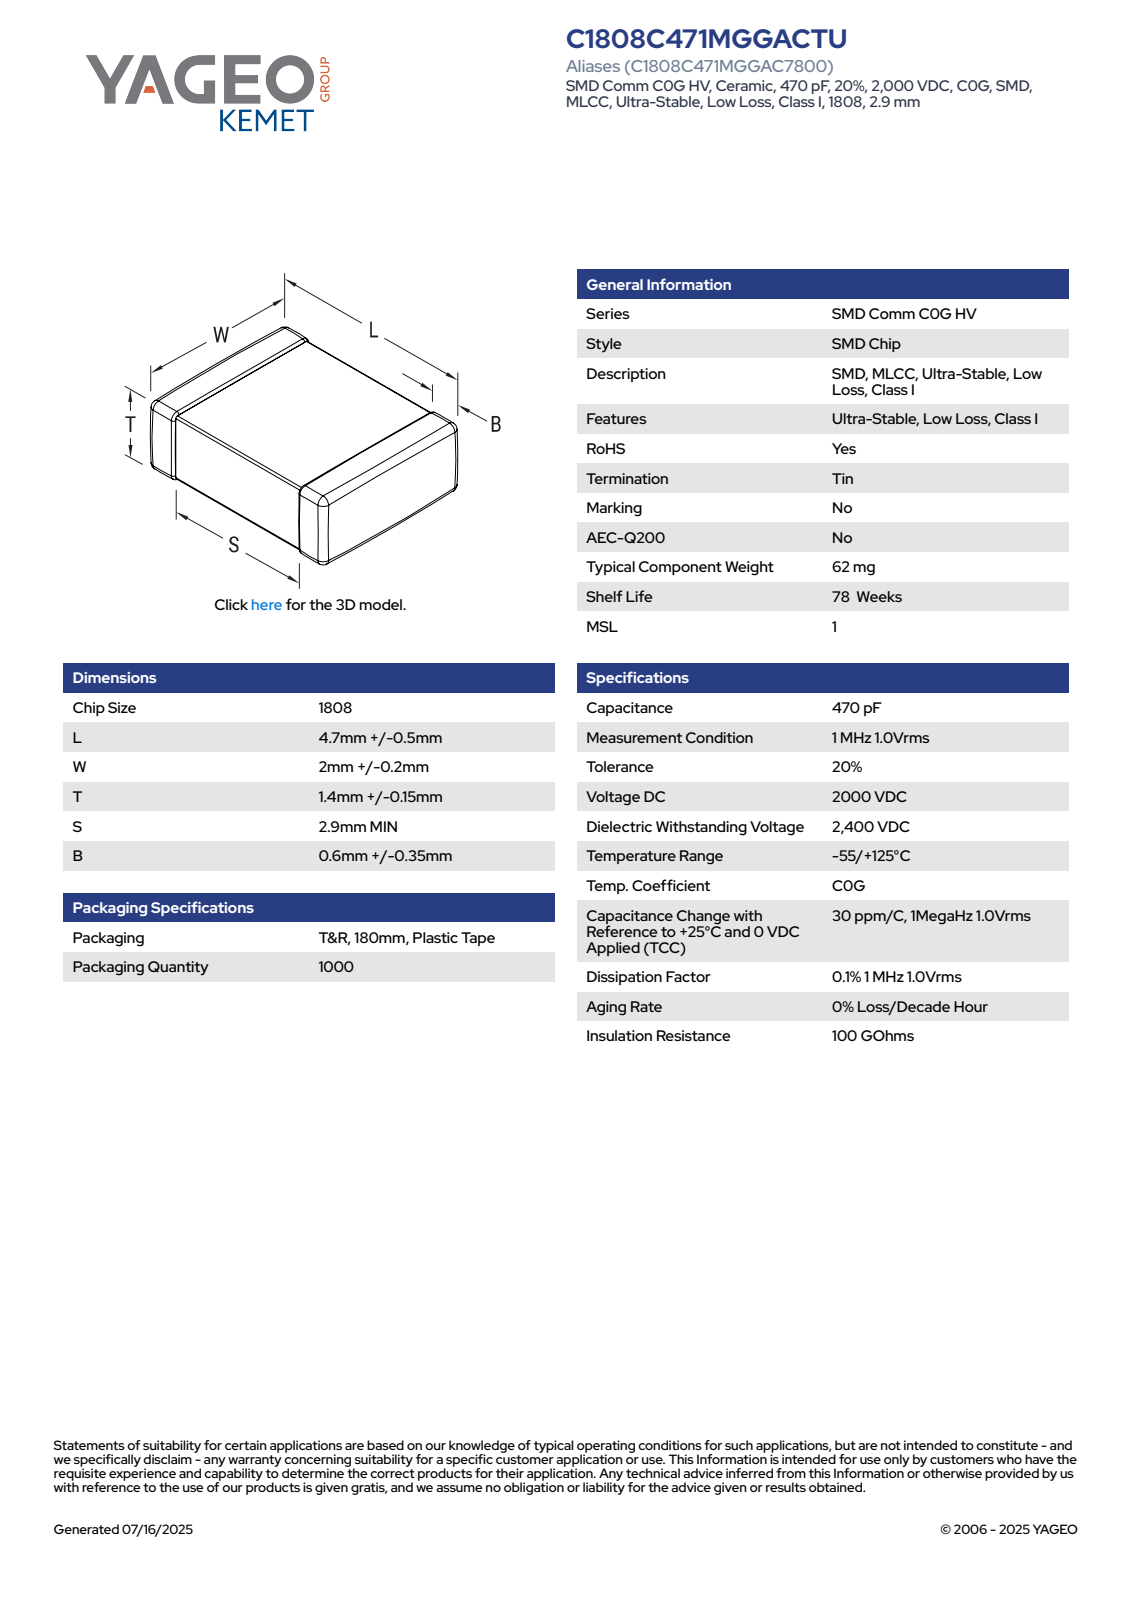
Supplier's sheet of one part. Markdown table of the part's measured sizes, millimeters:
| quantity | value |
| --- | --- |
| part name | CCS_CCSTD_1808_L5.2W2.2T1.55B0.6 |
| STEP written by | SolidWorks 2021 (AUTOMOTIVE_DESIGN) |
| units | millimeters |
| bodies | 4 solids, 125 faces (71 planar, 38 cylindrical, 16 other) |
| overall size | 5.2 × 2.2 × 1.55 |
| volume | 17 mm³ |
| surface area | 45 mm² |
| main face-to-face distances | 1.5, 1.45, 2.15, 2.1, 1.55, 5.2, 2.2, 1.51, 1.46, 0.33 |
